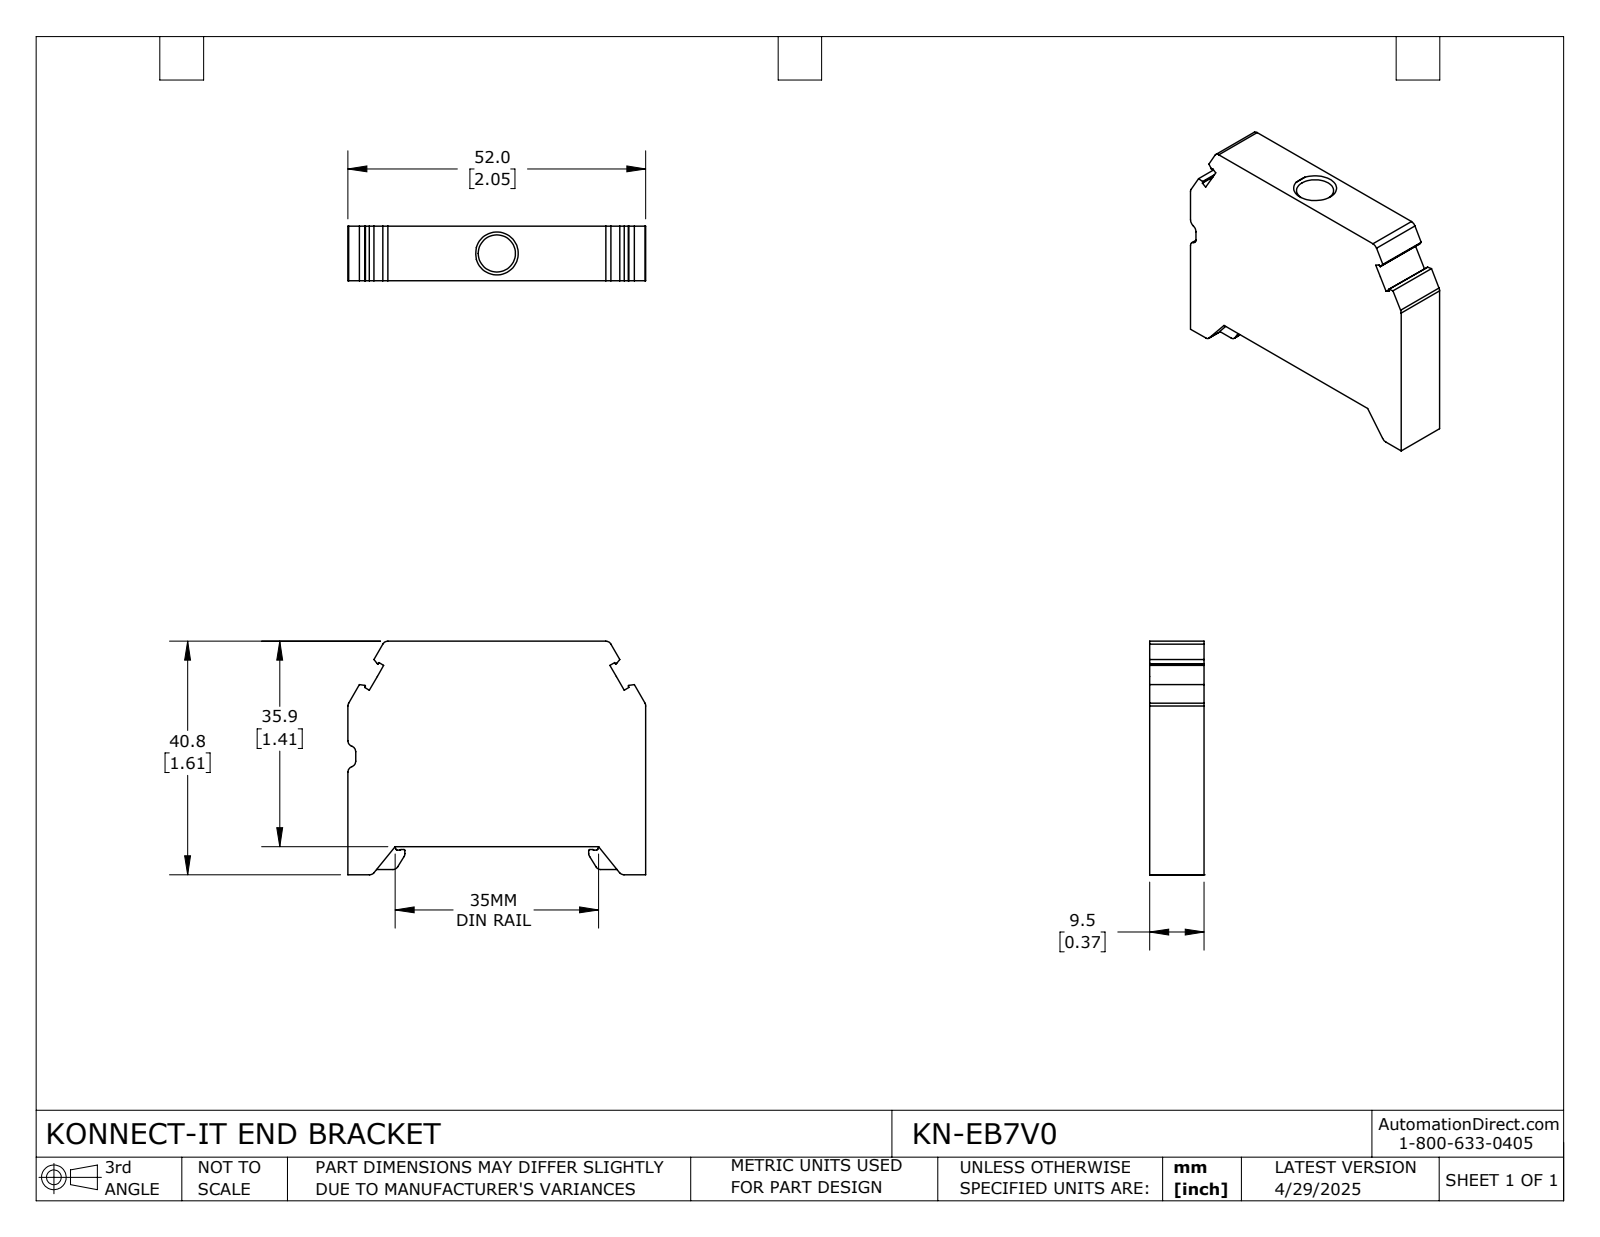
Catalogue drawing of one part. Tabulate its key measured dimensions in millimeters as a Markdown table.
| quantity | value |
| --- | --- |
| part name | KN-EB7V0 |
| STEP written by | SolidWorks 2024 (CONFIG_CONTROL_DESIGN) |
| units | millimeters |
| bodies | 1 solid, 105 faces (59 planar, 43 cylindrical, 3 other) |
| overall size | 52 × 40.77 × 9.5 |
| volume | 17 418 mm³ |
| surface area | 5 580 mm² |
| partial cylindrical surfaces (radius × count) | 1 × 14, 0.1 × 8, 0.2 × 4, 2.94 × 2 |
| main face-to-face distances | 9.5, 35.85, 52, 1.99, 4.92, 40.77, 2.2, 7.3, 3.2, 6.3 |
